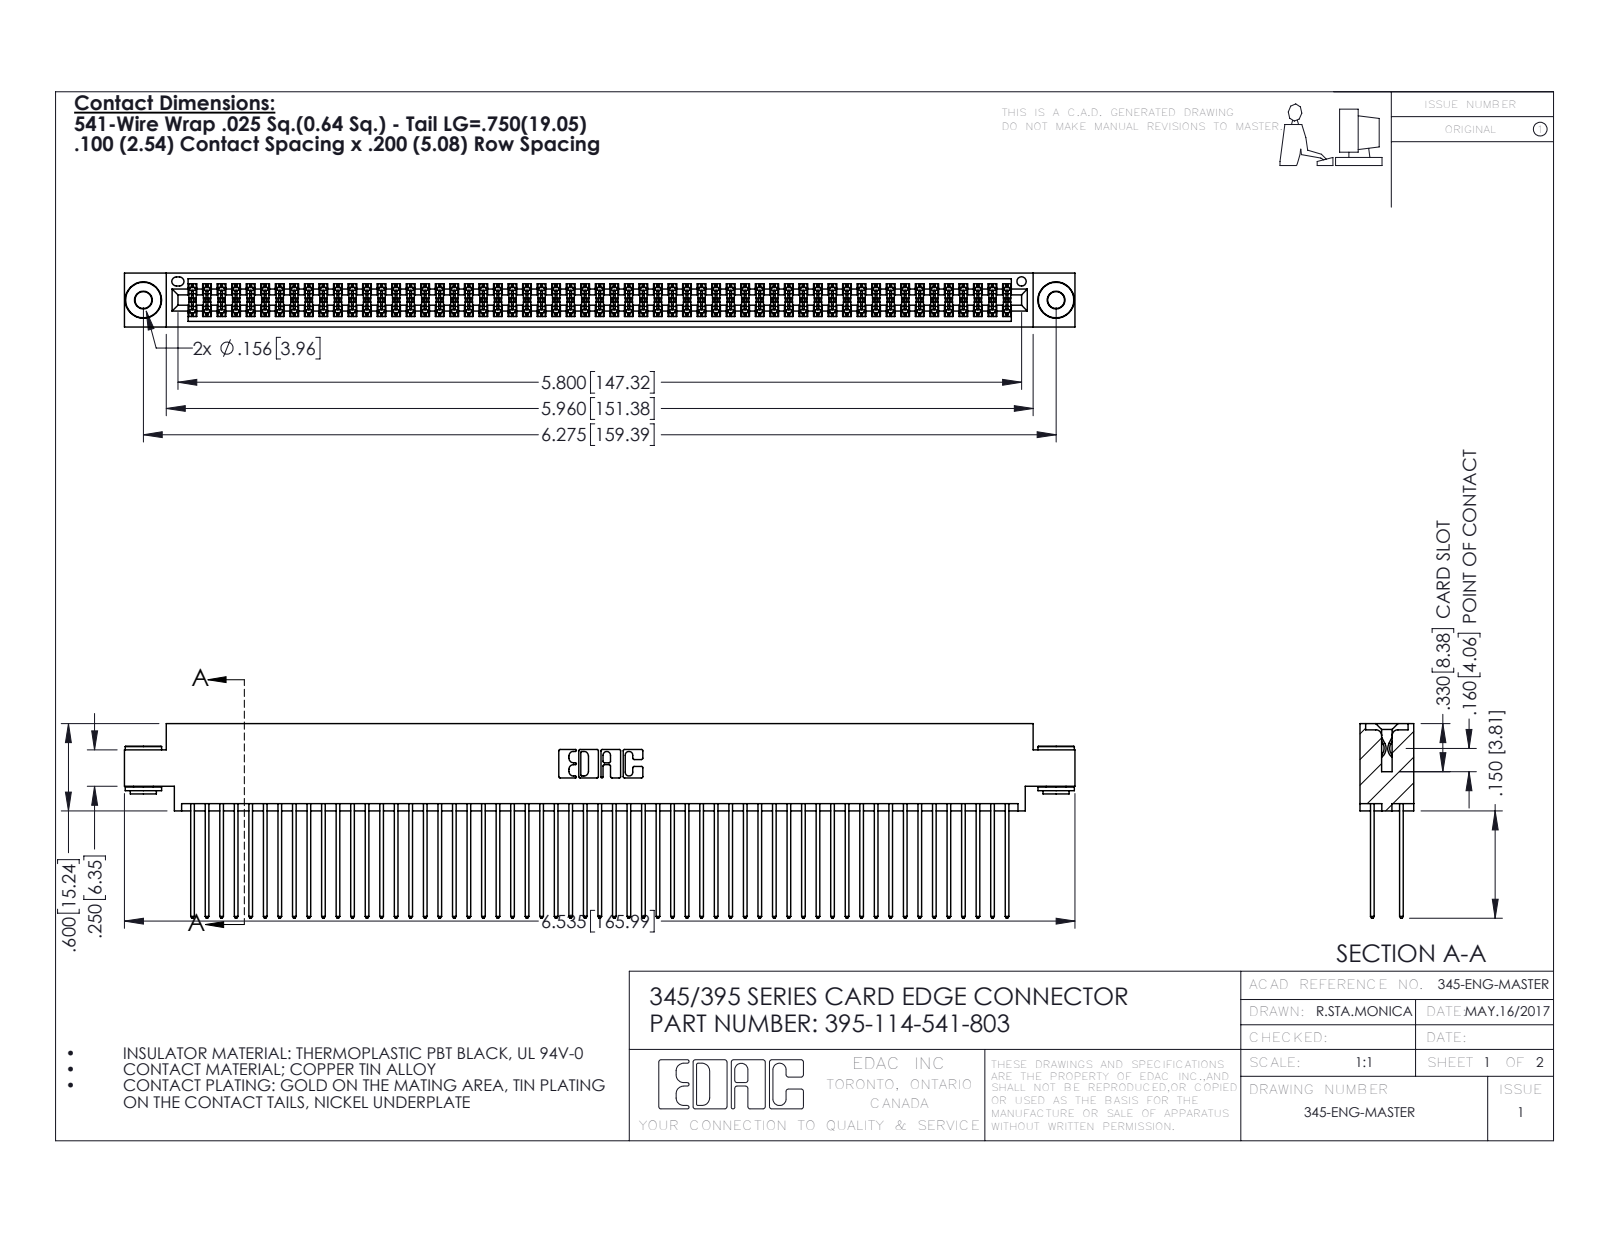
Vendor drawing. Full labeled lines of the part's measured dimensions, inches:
Part name (STEP PRODUCT): 345-250-002_345-250-002-102; 345-292-001_345-293-141; 395-114-541-803; 345 Part_0.170 Offset - 0.156 Dia-TH
STEP written by: SolidWorks 2016 (CONFIG_CONTROL_DESIGN)
Units: inches
Bodies: 117 solids, 5868 faces (3856 planar, 2004 cylindrical, 8 other)
Overall size (bounding box): 6.535 × 1.337 × 0.37
Volume: 1.027 in³ · Surface area: 44.3 in²
Round holes (diameter × count): ⌀0.116 ×2, ⌀0.156 ×2, ⌀0.064 ×1
Round bosses / shafts (diameter × count): ⌀0.25 ×2, ⌀0.18 ×2, ⌀0.136 ×2
Partial cylindrical surfaces — rounded edges, fillets, slot ends (radius × count): R0.006 ×171, R0.01 ×114, R0.01 ×22, R0.007 ×6, R0.031 ×6, R0.026 ×3, R0.014 ×2, R0.019 ×2
Main face-to-face distances: 0.072, 0.298, 0.2, 0.098, 0.272, 0.025, 0.225, 0.37, 0.175, 0.149
Hole centre spacings: 0.27, 6.039, 6.275
